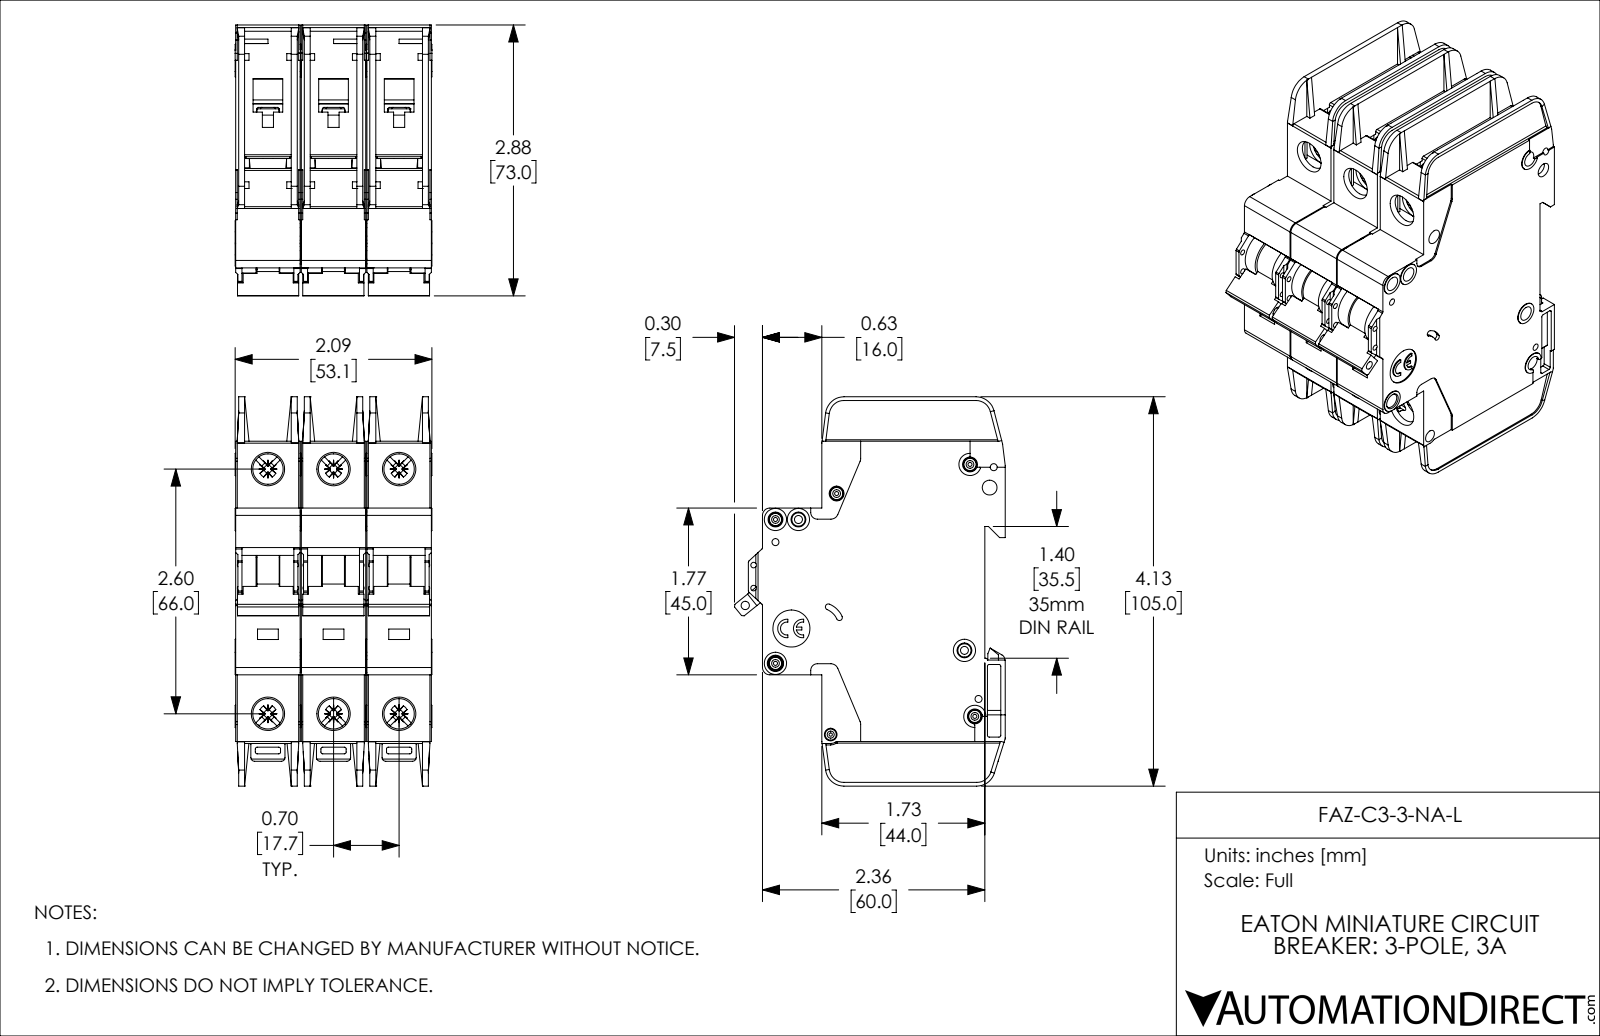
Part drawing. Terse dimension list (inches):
name: FAZ-C3-3-NA-L
written by: SolidWorks 2019 (AUTOMOTIVE_DESIGN)
unit: in
bodies: 3 solids, 3381 faces (2013 planar, 1071 cylindrical, 297 other)
size: 4.134 × 2.876 × 2.091
volume: 14.05 in³; area: 123 in²
holes: 8× ⌀0.157, 6× ⌀0.323, 5× ⌀0.043, 4× ⌀0.075, 2× ⌀0.059, 2× ⌀0.085, 1× ⌀0.035, 1× ⌀0.089, 1× ⌀0.098, 1× ⌀0.134, 1× ⌀0.394
bosses: 5× ⌀0.13, 4× ⌀0.236, 4× ⌀0.118, 3× ⌀0.098
rounds: 72× R0.02, 30× R0.016, 18× R0.039, 12× R0.043, 12× R0.079, 6× R0.008, 6× R0.01, 6× R0.028
face distances: 0.697, 0.047, 1.394, 0.685, 0.591, 1.382, 0.744, 0.65, 0.106, 0.094
hole spacings: 0.697, 2.69, 2.598, 0.244, 0.537, 0.87, 1.394, 2.948
